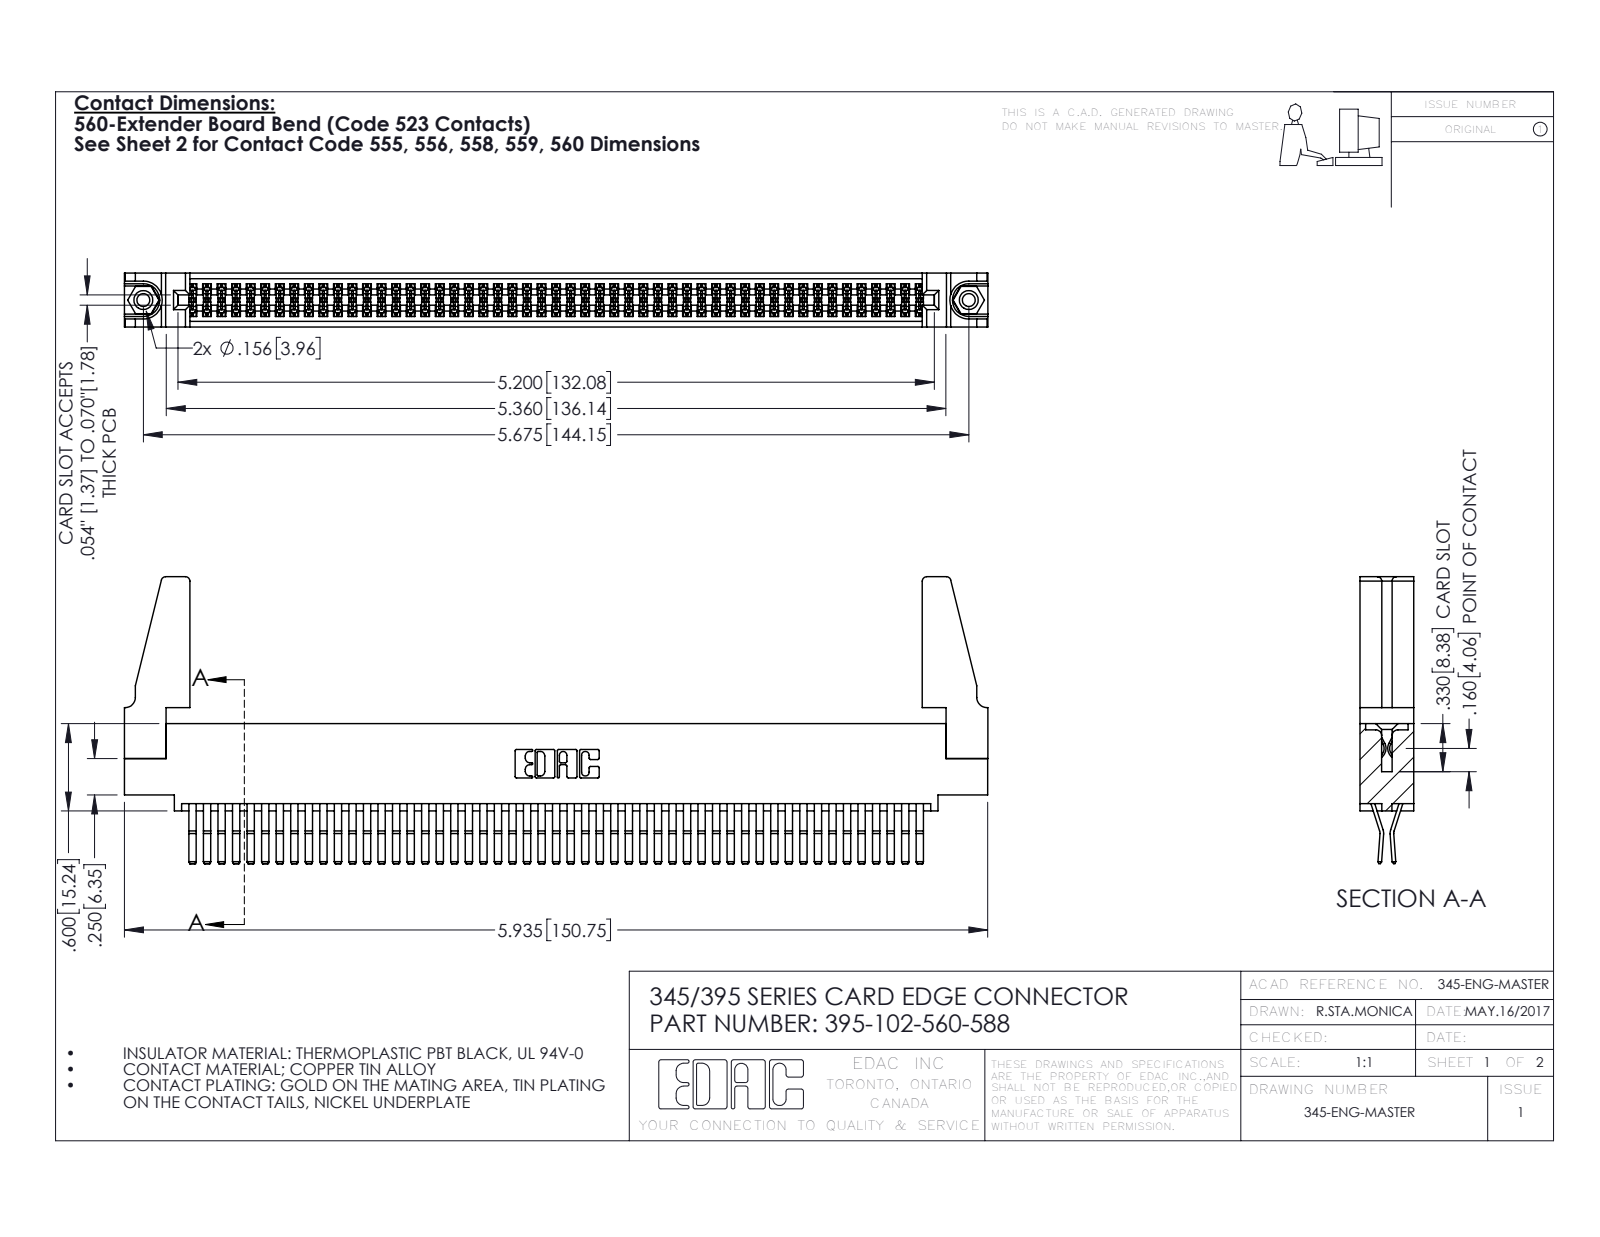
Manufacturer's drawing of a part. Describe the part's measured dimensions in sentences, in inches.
The part is named "345-220-078_345-220-088; 345-292-001_560 Tail; 345-250-001_345-250-001-102; 345 Part_0.110 Offset - 0.156 Dia-TH (+1 more)". Its 3-D file was written by "SolidWorks 2016 (CONFIG_CONTROL_DESIGN)". It is 107 solids with 5558 faces: 3522 planar, 2020 cylindrical and 16 other. Overall it measures 5.936 by 1.972 by 0.37 inches. Its volume is 1.134 cubic inches and its surface area 43.03 square inches. Round holes: 2 of diameter 0.089, 2 of diameter 0.125, 2 of diameter 0.156, 1 of diameter 0.064. Round bosses or shafts: 2 of diameter 0.155. Partial cylindrical surfaces (rounded edges, fillets, slot ends): 154 of radius 0.006, 22 of radius 0.01, 8 of radius 0.03, 6 of radius 0.007, 6 of radius 0.031, 3 of radius 0.026, 2 of radius 0.01, 2 of radius 0.014. The main face-to-face distances are 0.072, 0.298, 0.025, 0.37, 0.2, 0.098, 0.272, 0.225, 0.175, 0.149. The hole center spacings are 0.27, 5.439, 5.675.
